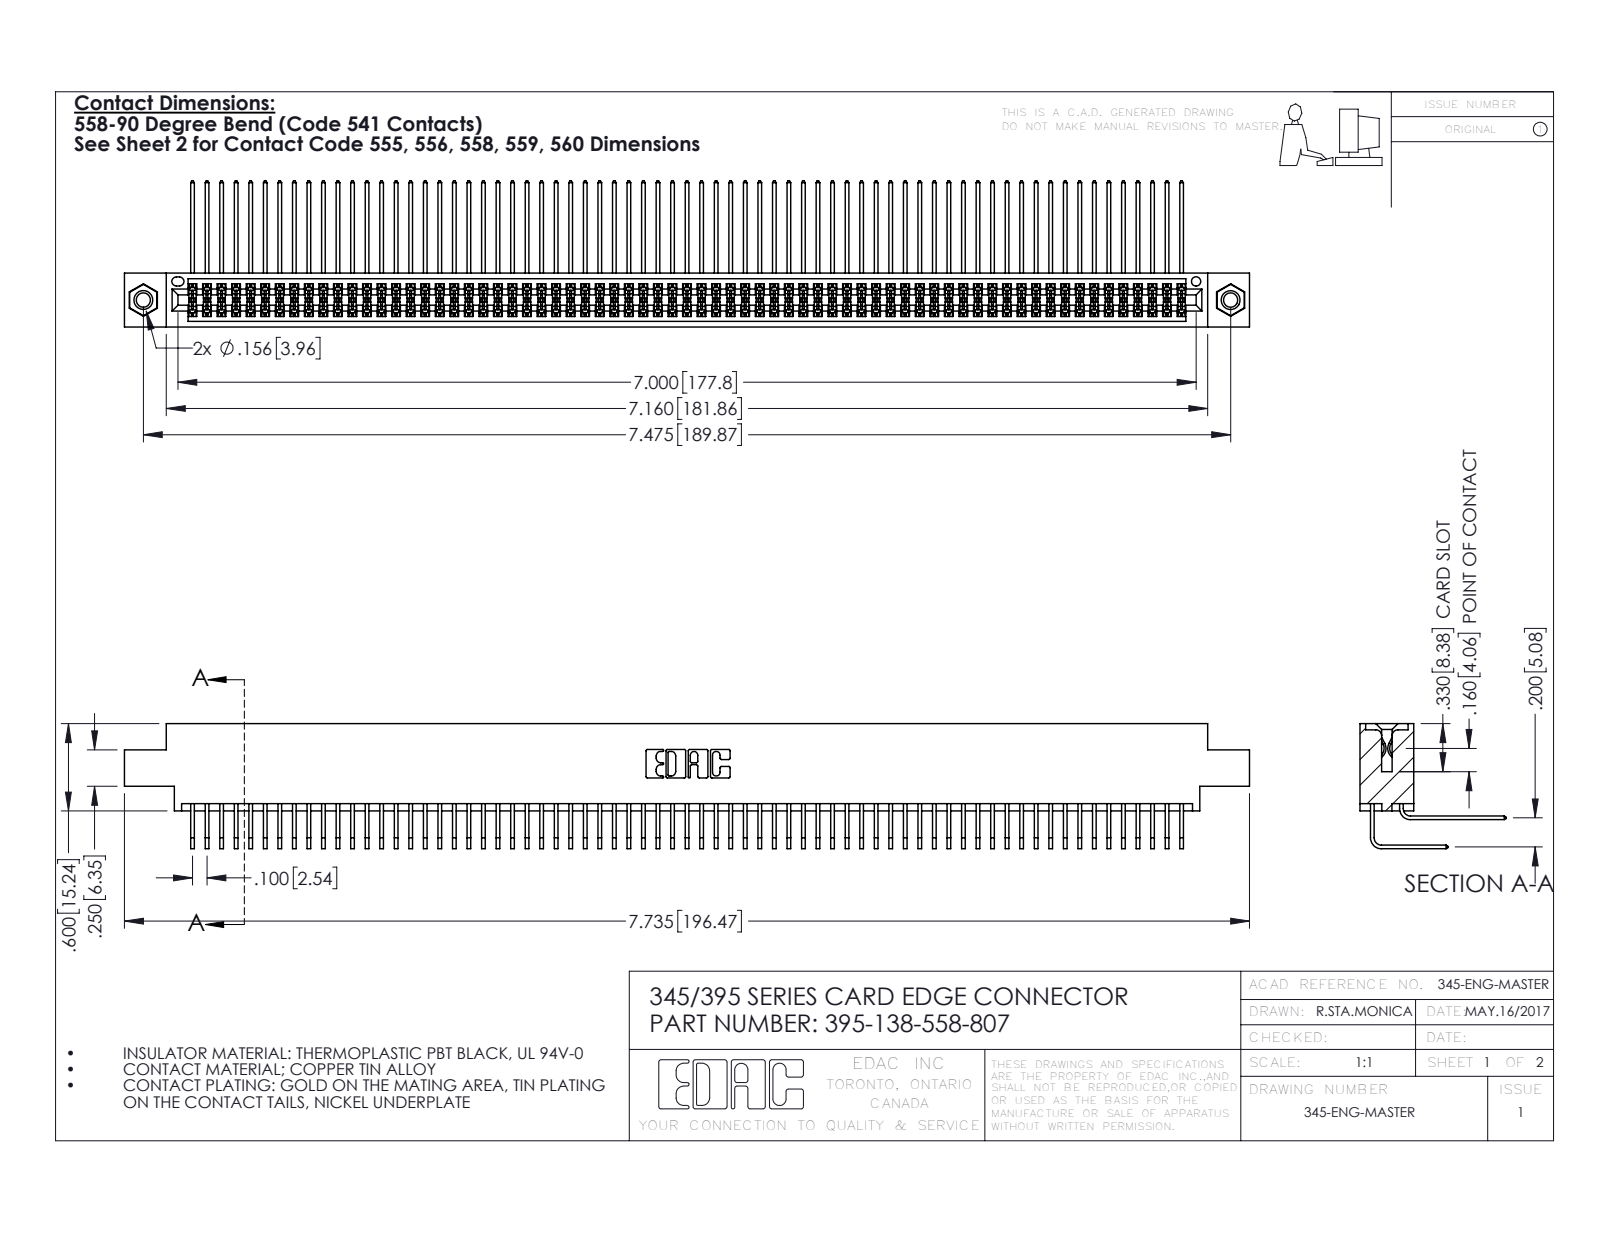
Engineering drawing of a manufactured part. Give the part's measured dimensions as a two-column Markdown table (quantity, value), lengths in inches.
| quantity | value |
| --- | --- |
| part name | 345-292-001_558 559 Tail - 1; 345-250-001_345-250-005-103; 345 Part_0.170 Offset - 0.156 Dia-TI; 345-292-001_558 Tail - 2 (+1 more) |
| STEP written by | SolidWorks 2016 (CONFIG_CONTROL_DESIGN) |
| units | inches |
| bodies | 141 solids, 7366 faces (4946 planar, 2404 cylindrical, 16 other) |
| overall size | 7.735 × 1.005 × 0.859 |
| volume | 1.221 in³ |
| surface area | 52.71 in² |
| round holes (diameter × count) | 0.098 × 2, 0.125 × 2, 0.156 × 2, 0.064 × 1 |
| round bosses / shafts (diameter × count) | 0.155 × 2 |
| partial cylindrical surfaces (radius × count) | 0.006 × 275, 0.01 × 22, 0.007 × 6, 0.031 × 6, 0.026 × 3, 0.014 × 2, 0.019 × 2, 0.022 × 2 |
| main face-to-face distances | 0.072, 0.298, 0.2, 0.37, 0.098, 0.272, 0.025, 0.225, 0.175, 0.025 |
| hole center spacings | 0.27, 7.239, 7.475 |
